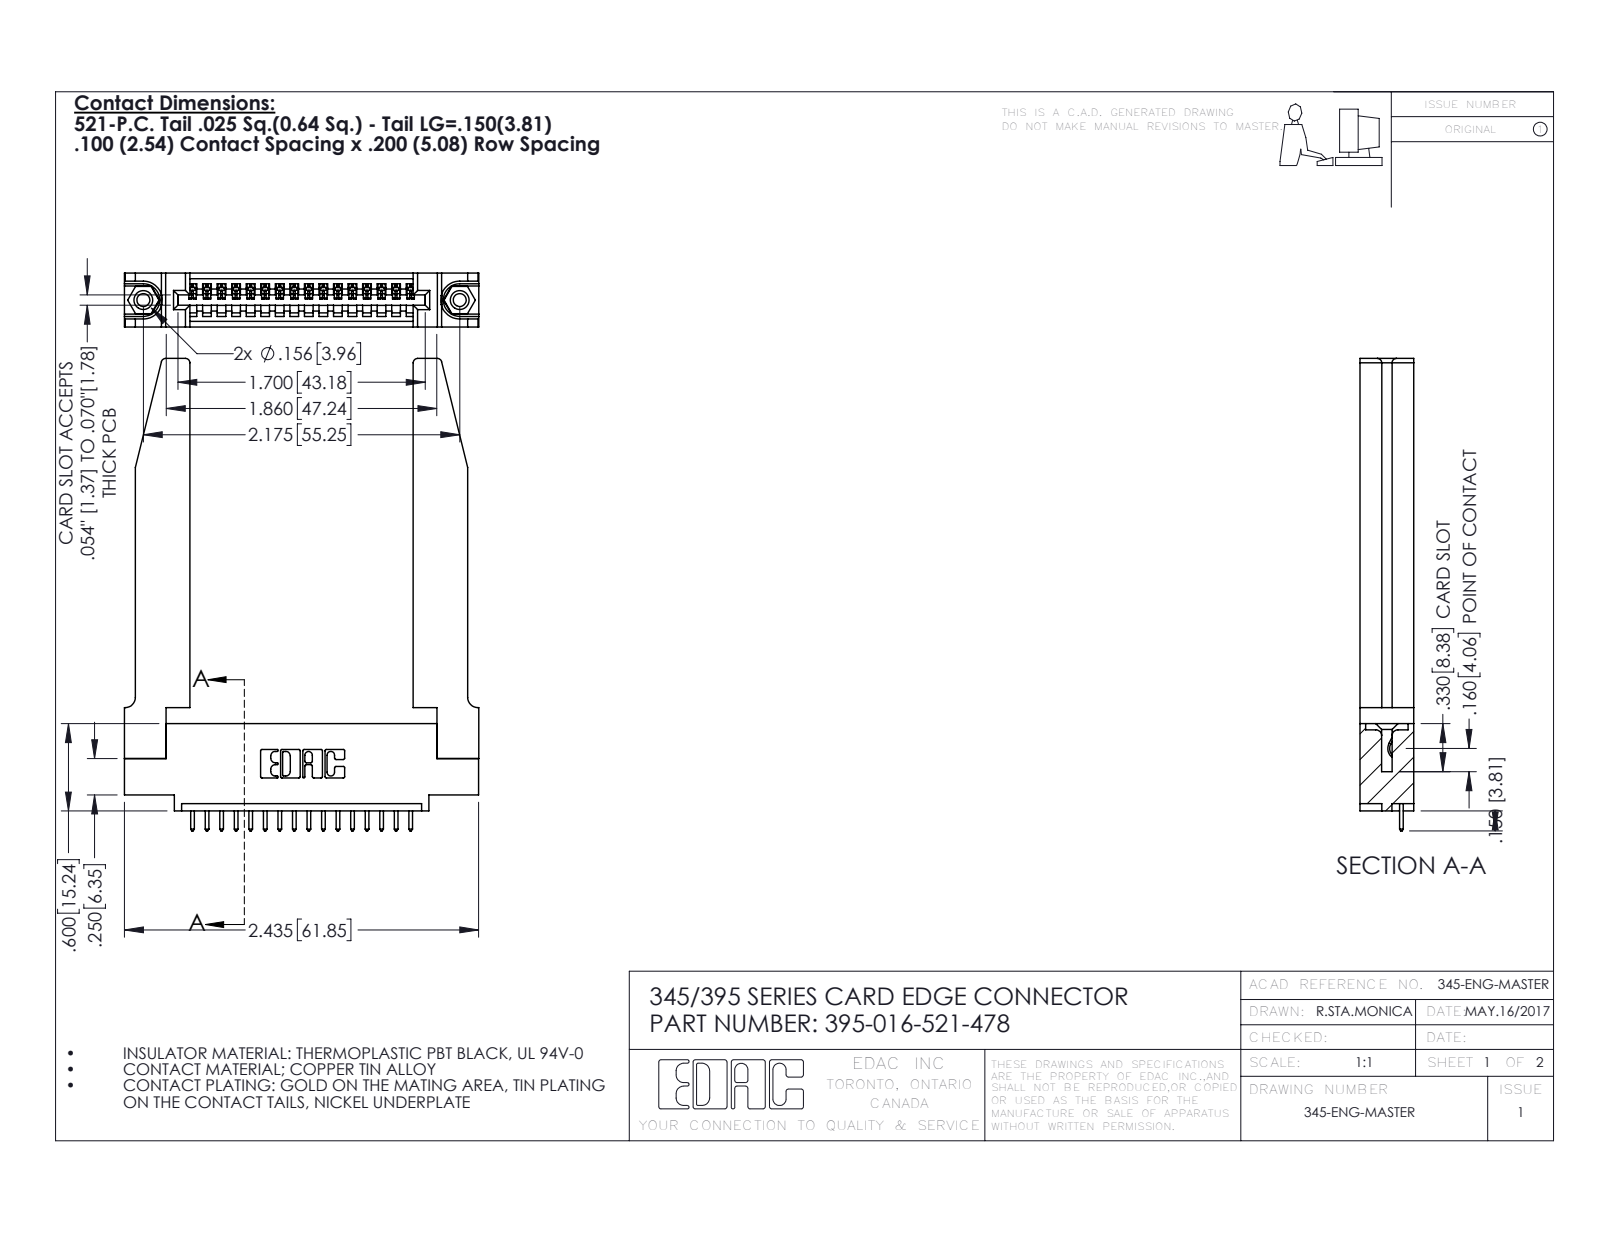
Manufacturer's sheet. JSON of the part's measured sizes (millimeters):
{"part_name": "345-292-001_345-293-121; 395-016-521-478; 345 Part_0.110 Offset - 0.156 Dia-TH; 345-250-001_345-250-001-102 (+1 more)", "step_written_by": "SolidWorks 2016 (CONFIG_CONTROL_DESIGN)", "units": "millimeters", "bodies": {"solids": 21, "faces": 1292, "planar": 866, "cylindrical": 374, "other": 52}, "overall_size": [82.5, 61.9, 9.4], "volume_mm3": 13300, "surface_area_mm2": 13770, "round_holes": [[2.3, 2], [3.2, 2], [4, 2], [1.6, 1]], "round_bosses_or_shafts": [[3.9, 2]], "partial_cylinders_radius": [[0.2, 32], [0.3, 32], [0.3, 22], [0.8, 8], [0.2, 6], [0.8, 6], [0.7, 3], [0.8, 2]], "face_to_face_distances": [9.4, 1.8, 7.6, 3.8, 3.8, 5.1, 5.6, 2, 2.5, 6.9], "hole_center_spacings": [6.9, 49.3, 55.2]}
